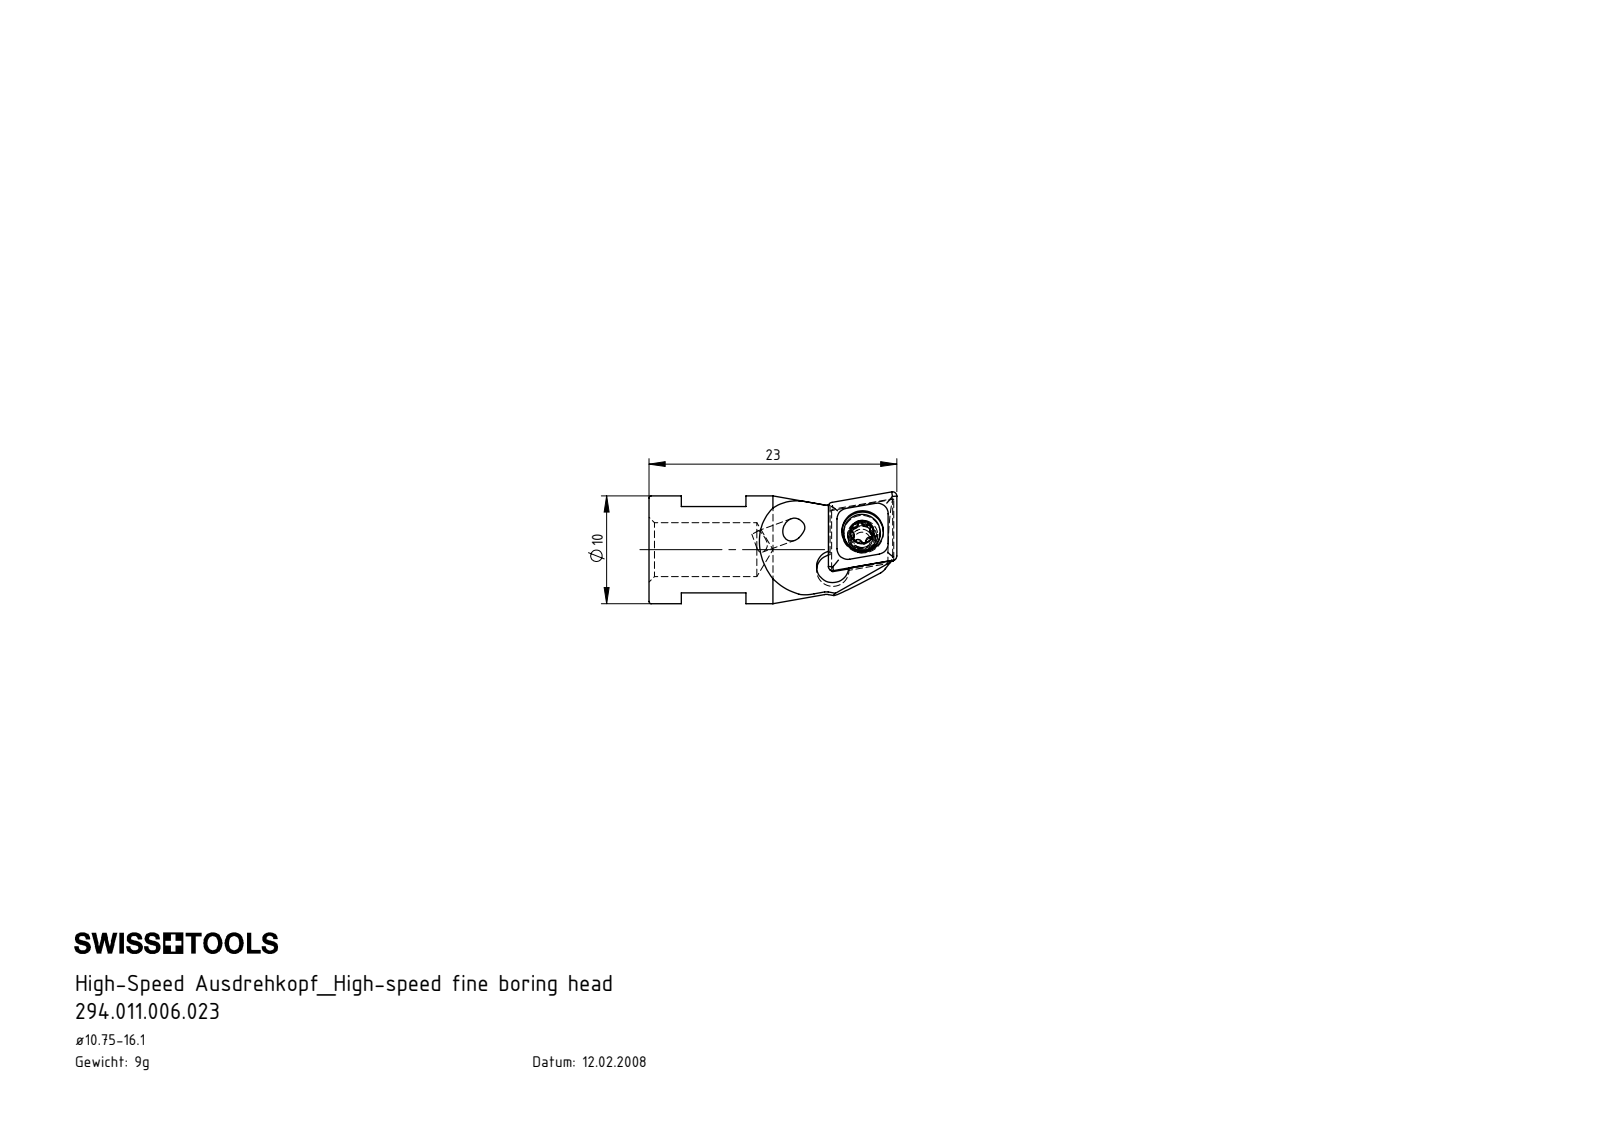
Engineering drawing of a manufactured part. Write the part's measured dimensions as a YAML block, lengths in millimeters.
part_name: "HS6-A11.K11.023_B; HS6.A11.K11.023; WCA-ER2.001.005_A; CCMT060204"
step_written_by: "SolidWorks 2017 (AUTOMOTIVE_DESIGN)"
units: millimeters
bodies: {solids: 3, faces: 129, planar: 34, cylindrical: 35, other: 60}
overall_size: [23, 10.38, 10.13]
volume: 1063
surface_area: 1148
round_holes:
  - {diameter: 2, count: 1}
  - {diameter: 2.05, count: 1}
  - {diameter: 2.8, count: 1}
  - {diameter: 3.85, count: 1}
  - {diameter: 5, count: 1}
round_bosses_or_shafts:
  - {diameter: 10, count: 1}
  - {diameter: 3.4, count: 1}
  - {diameter: 2.5, count: 1}
partial_cylinders:
  - {radius: 0.21, count: 6}
  - {radius: 0.36, count: 5}
  - {radius: 0.36, count: 1}
  - {radius: 1.4, count: 1}
  - {radius: 1.5, count: 1}
  - {radius: 2, count: 1}
face_to_face_distances: [8.01, 2.29, 2.38, 9, 3, 6, 16.8, 13.8, 7.8, 1.48]
